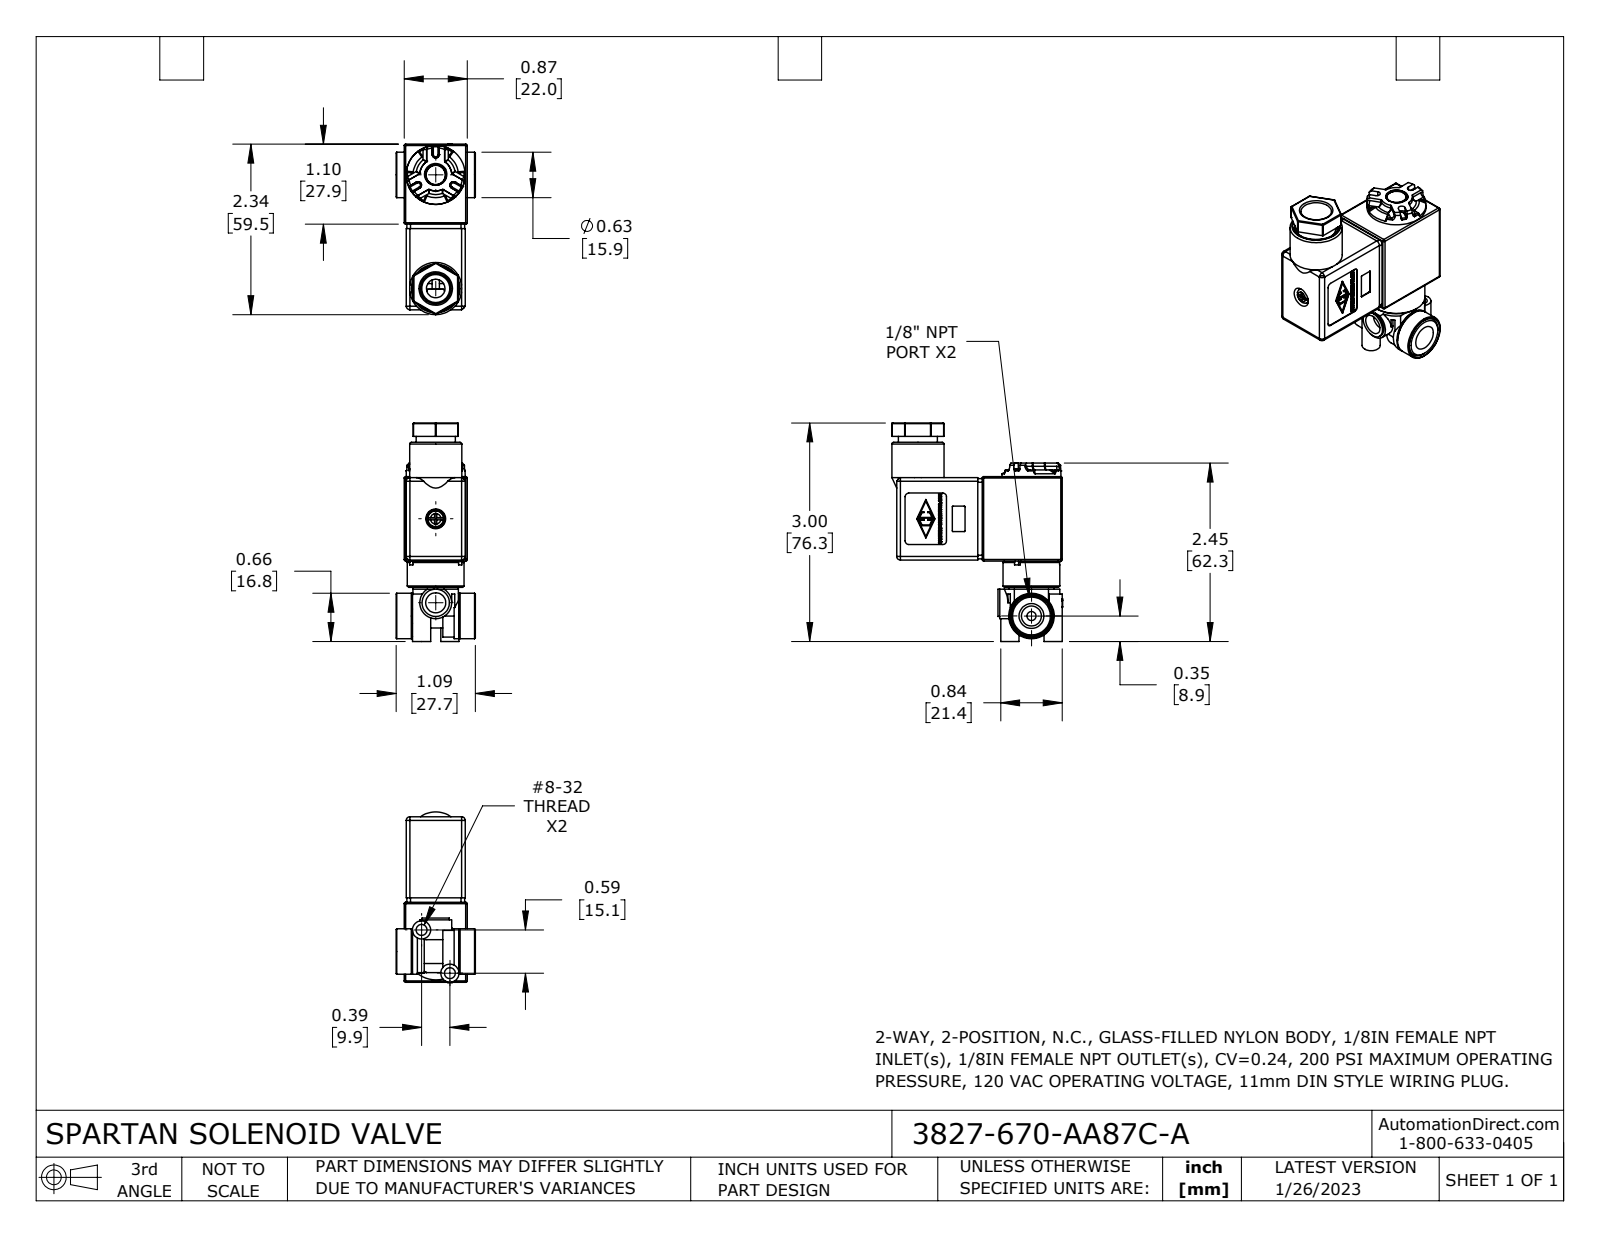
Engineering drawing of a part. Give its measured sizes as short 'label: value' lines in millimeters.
name: 3827-670-AA87C-A
written by: SolidWorks 2021 (CONFIG_CONTROL_DESIGN)
unit: mm
bodies: 4 solids, 3303 faces (2599 planar, 245 cylindrical, 459 other)
size: 76.3 × 59.7 × 27.7
volume: 38 870 mm³; area: 24 880 mm²
holes: 2× ⌀2.5, 2× ⌀3.2, 2× ⌀3.8, 1× ⌀1.6, 1× ⌀2.6, 1× ⌀2.9, 1× ⌀4.2, 1× ⌀5.2, 1× ⌀6.5, 1× ⌀6.8, 1× ⌀6.9, 1× ⌀7
bosses: 3× ⌀6.4, 2× ⌀15.9, 1× ⌀19.8, 1× ⌀18.2, 1× ⌀15, 1× ⌀14.2, 1× ⌀13.7, 1× ⌀13.1
rounds: 24× R0.5, 22× R0.3, 22× R1.3, 6× R0.4, 4× R0.9, 3× R1.1, 2× R0.6, 2× R0.7
face distances: 1.5, 1.7, 2.2, 19.8, 1.3, 0.7, 21.3, 19.1, 19.6, 22
hole spacings: 9, 4.4, 5.8, 6.3, 13, 14.1, 18, 18.7
